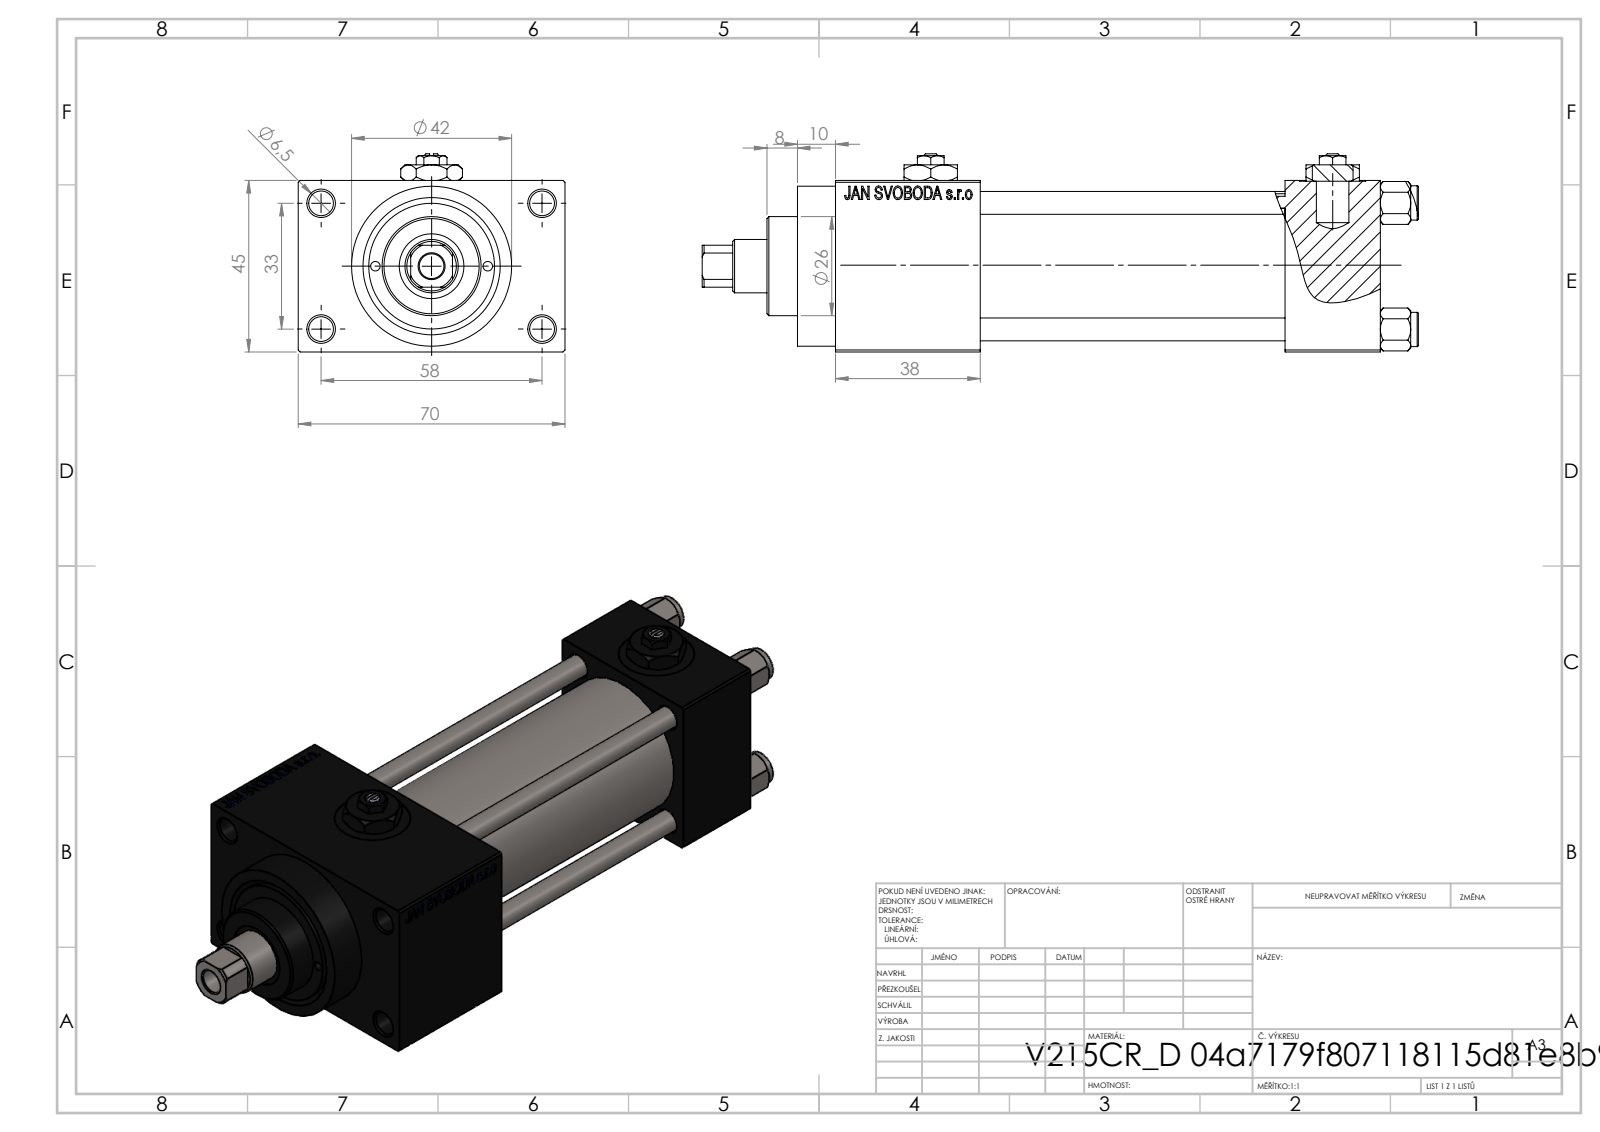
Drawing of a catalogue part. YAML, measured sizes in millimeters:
part_name: "V215CR_D_Body; V215_VC_A; Zatka_pro_OIL_PORT; NUT_M5_D (+2 more)"
step_written_by: "SolidWorks 2019 (CONFIG_CONTROL_DESIGN)"
units: millimeters
bodies: {solids: 13, faces: 1209, planar: 544, cylindrical: 103, other: 562}
overall_size: [188, 70, 52]
volume: 246813
surface_area: 87298
round_holes:
  - {diameter: 6.5, count: 5}
  - {diameter: 6, count: 4}
  - {diameter: 13.16, count: 4}
  - {diameter: 20, count: 4}
  - {diameter: 7, count: 3}
  - {diameter: 2.5, count: 2}
  - {diameter: 14, count: 1}
  - {diameter: 17, count: 1}
  - {diameter: 24, count: 1}
  - {diameter: 32, count: 1}
  - {diameter: 33, count: 1}
round_bosses_or_shafts:
  - {diameter: 9, count: 4}
  - {diameter: 42, count: 1}
  - {diameter: 38, count: 1}
  - {diameter: 26, count: 1}
partial_cylinders:
  - {radius: 6.5, count: 1}
face_to_face_distances: [45, 25, 12.5, 80, 105, 57.5, 118, 38, 143, 70]
hole_center_spacings: [12.4, 16.7, 21.8, 23.48, 33.2, 33.37, 35.35, 35.47]
